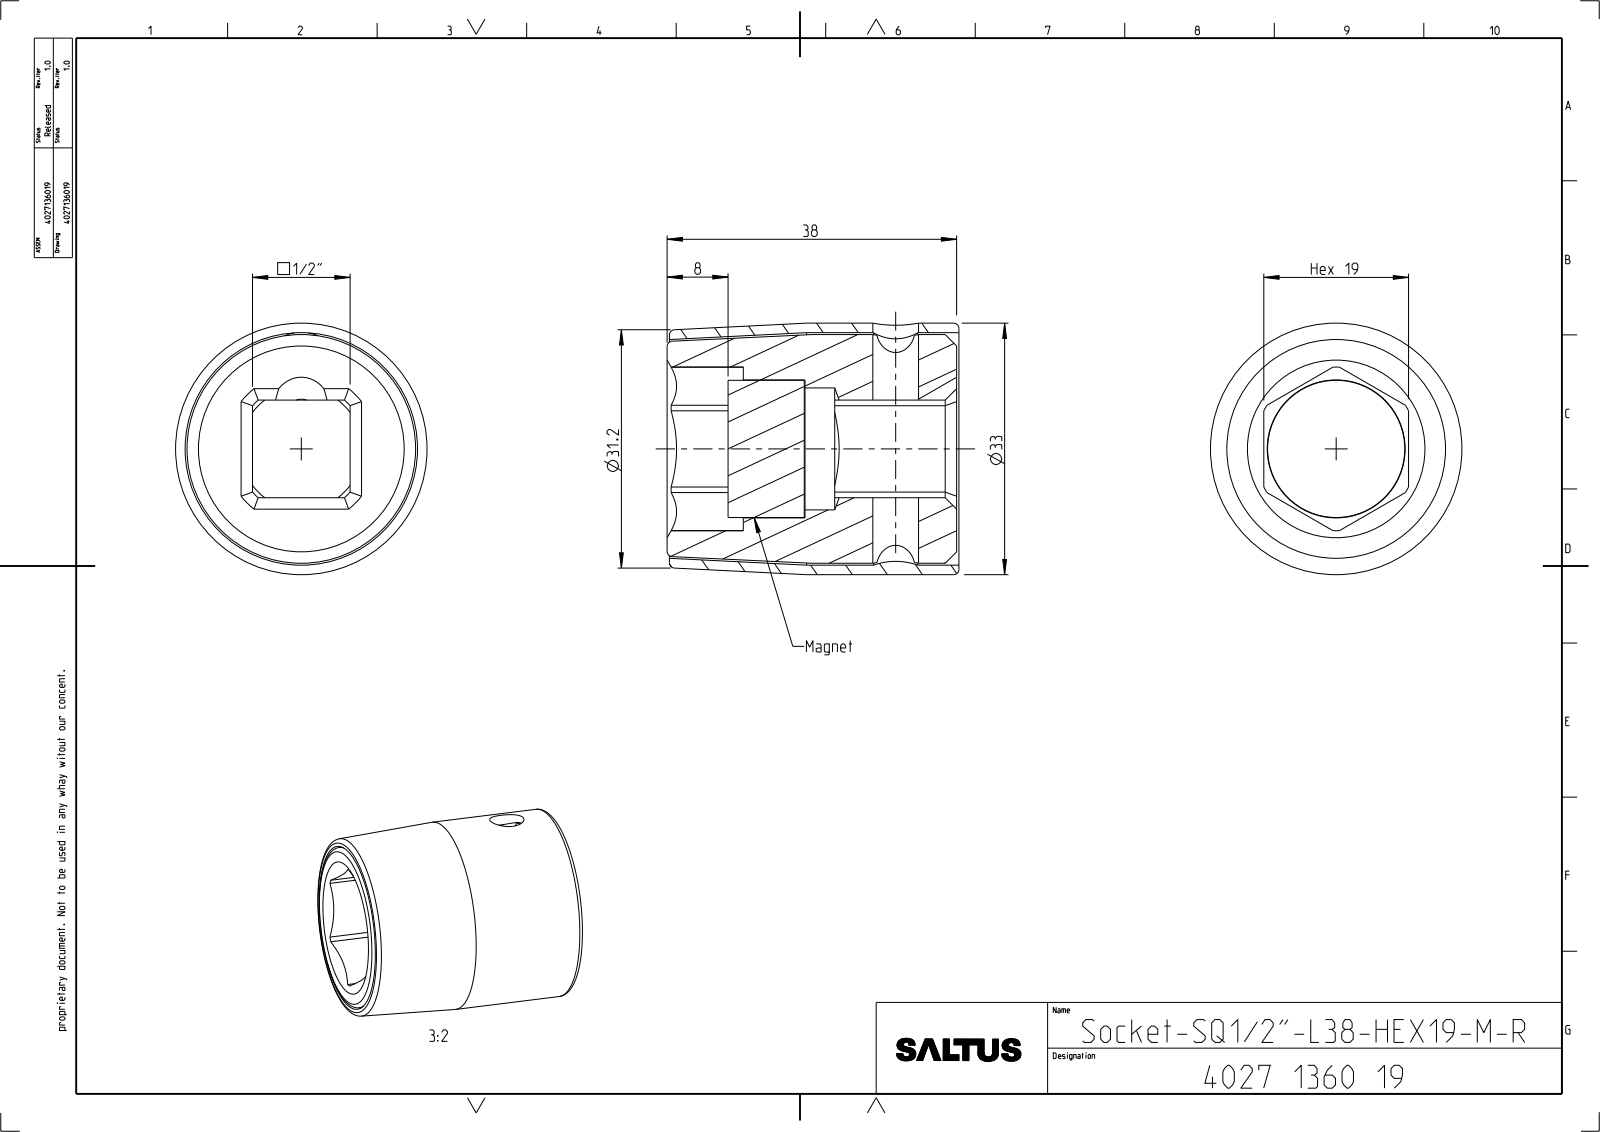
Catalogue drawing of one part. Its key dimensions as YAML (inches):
part_name: "4027130519; 4027043330; 4027136019_ASM"
step_written_by: "CREO PARAMETRIC BY PTC INC, 2022414 (CONFIG_CONTROL_DESIGN)"
units: inches
bodies: {solids: 3, faces: 87, planar: 27, cylindrical: 33, other: 27}
overall_size: [1.508, 1.299, 1.299]
volume: 1.434
surface_area: 23.91
round_holes:
  - {diameter: 0.236, count: 1}
  - {diameter: 0.63, count: 1}
  - {diameter: 0.713, count: 1}
  - {diameter: 1.201, count: 1}
round_bosses_or_shafts:
  - {diameter: 1.299, count: 1}
  - {diameter: 1.181, count: 1}
  - {diameter: 0.709, count: 1}
partial_cylinders:
  - {radius: 0.157, count: 1}
  - {radius: 0.337, count: 1}
  - {radius: 0.422, count: 1}
face_to_face_distances: [0.394, 0.505, 0.748, 0.787, 1.181, 0.315, 1.496, 0.122, 0.626, 0.709]
